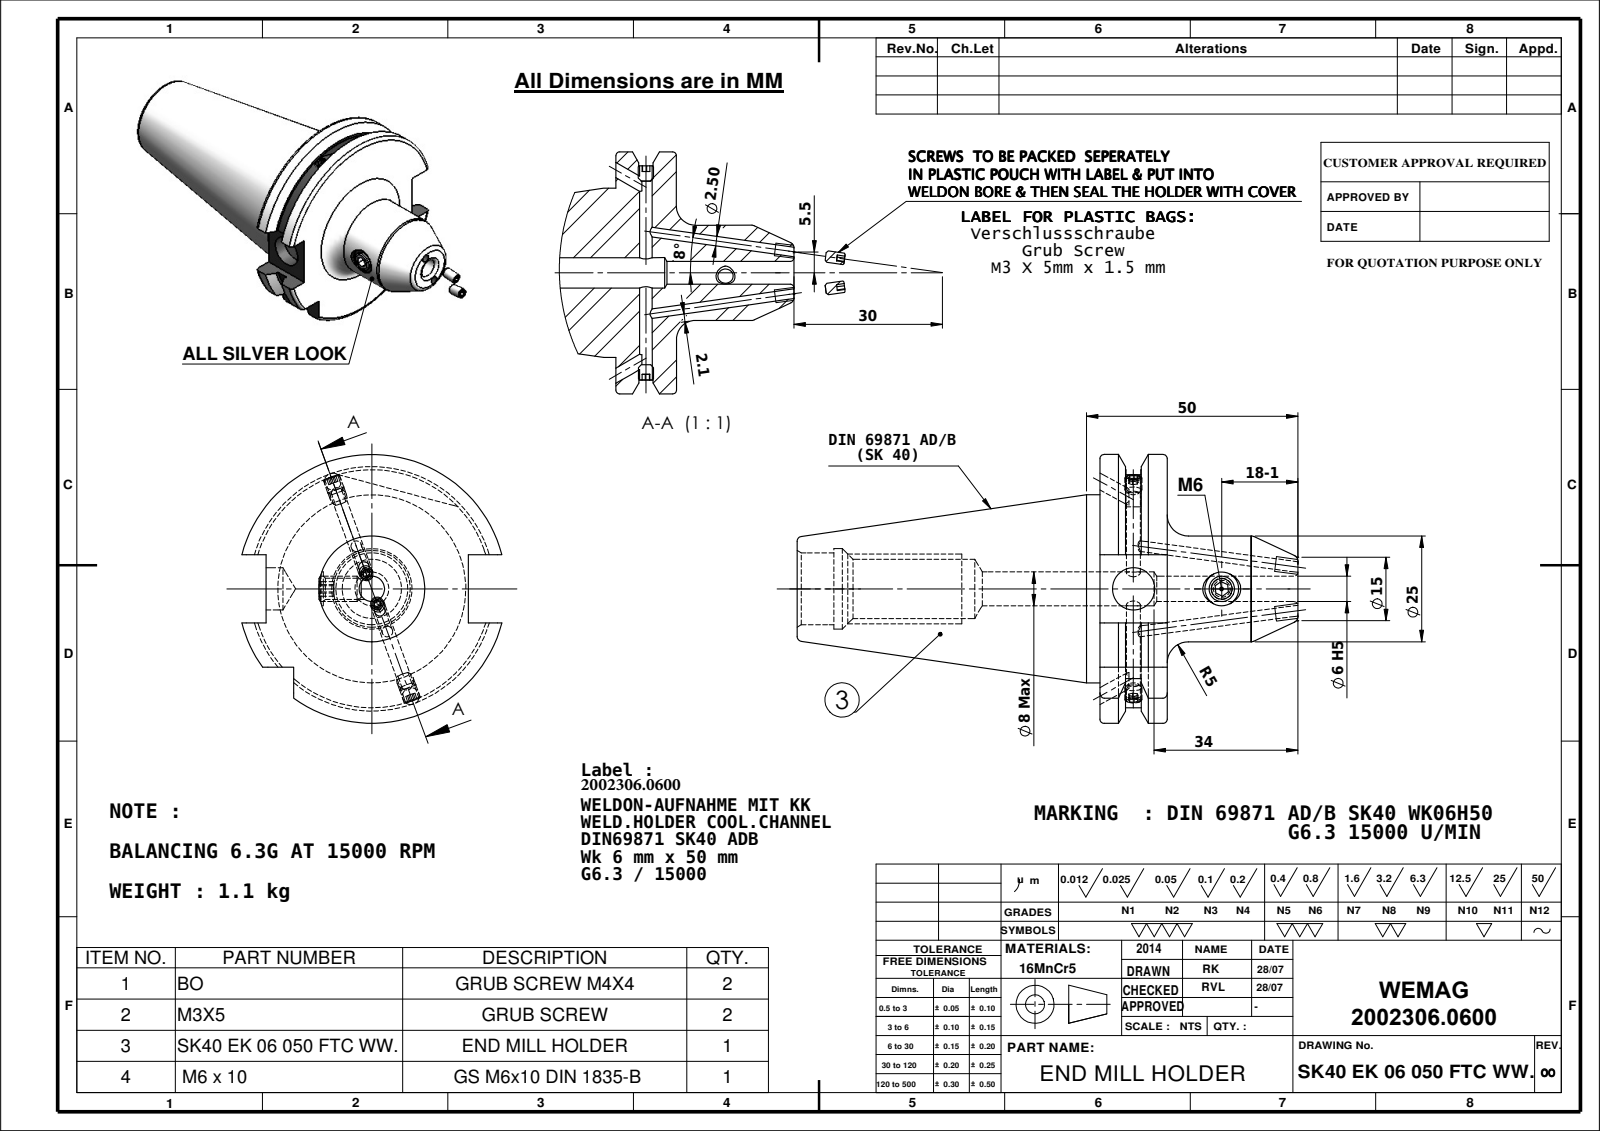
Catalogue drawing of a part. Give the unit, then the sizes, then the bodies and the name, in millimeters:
Units: millimetres
Overall size (bounding box): 131.83 × 63.55 × 61.48
Round holes (diameter × count): ⌀2.5 ×2, ⌀8 ×2, ⌀3.3 ×1, ⌀5 ×1, ⌀6 ×1, ⌀10 ×1, ⌀14 ×1, ⌀17 ×1, ⌀19 ×1
Round bosses / shafts (diameter × count): ⌀4 ×2, ⌀3 ×2, ⌀44.45 ×1, ⌀25 ×1, ⌀6 ×1
Partial cylindrical surfaces — rounded edges, fillets, slot ends (radius × count): R28.12 ×1, R31.77 ×1
Main face-to-face distances: 15.9, 16.1, 47.8, 71.6, 87.5, 77.63, 6.03, 9.87, 81.38, 9.78
Hole centre spacings: 20.85
Volume: 115 475 mm³ · Surface area: 24 262 mm²
Bodies: 6 solids, 190 faces (72 planar, 50 cylindrical, 68 other)
Part name (STEP PRODUCT): M6X10_DIN 913 - M6 x 10-N; M3X5_DIN 913 - M3 x 5-N; SK40 EK 06 050 FTC WW.; Copy of M4X4_DIN 913 - M4 x 4-N
STEP written by: SolidWorks 2009 (CONFIG_CONTROL_DESIGN)
